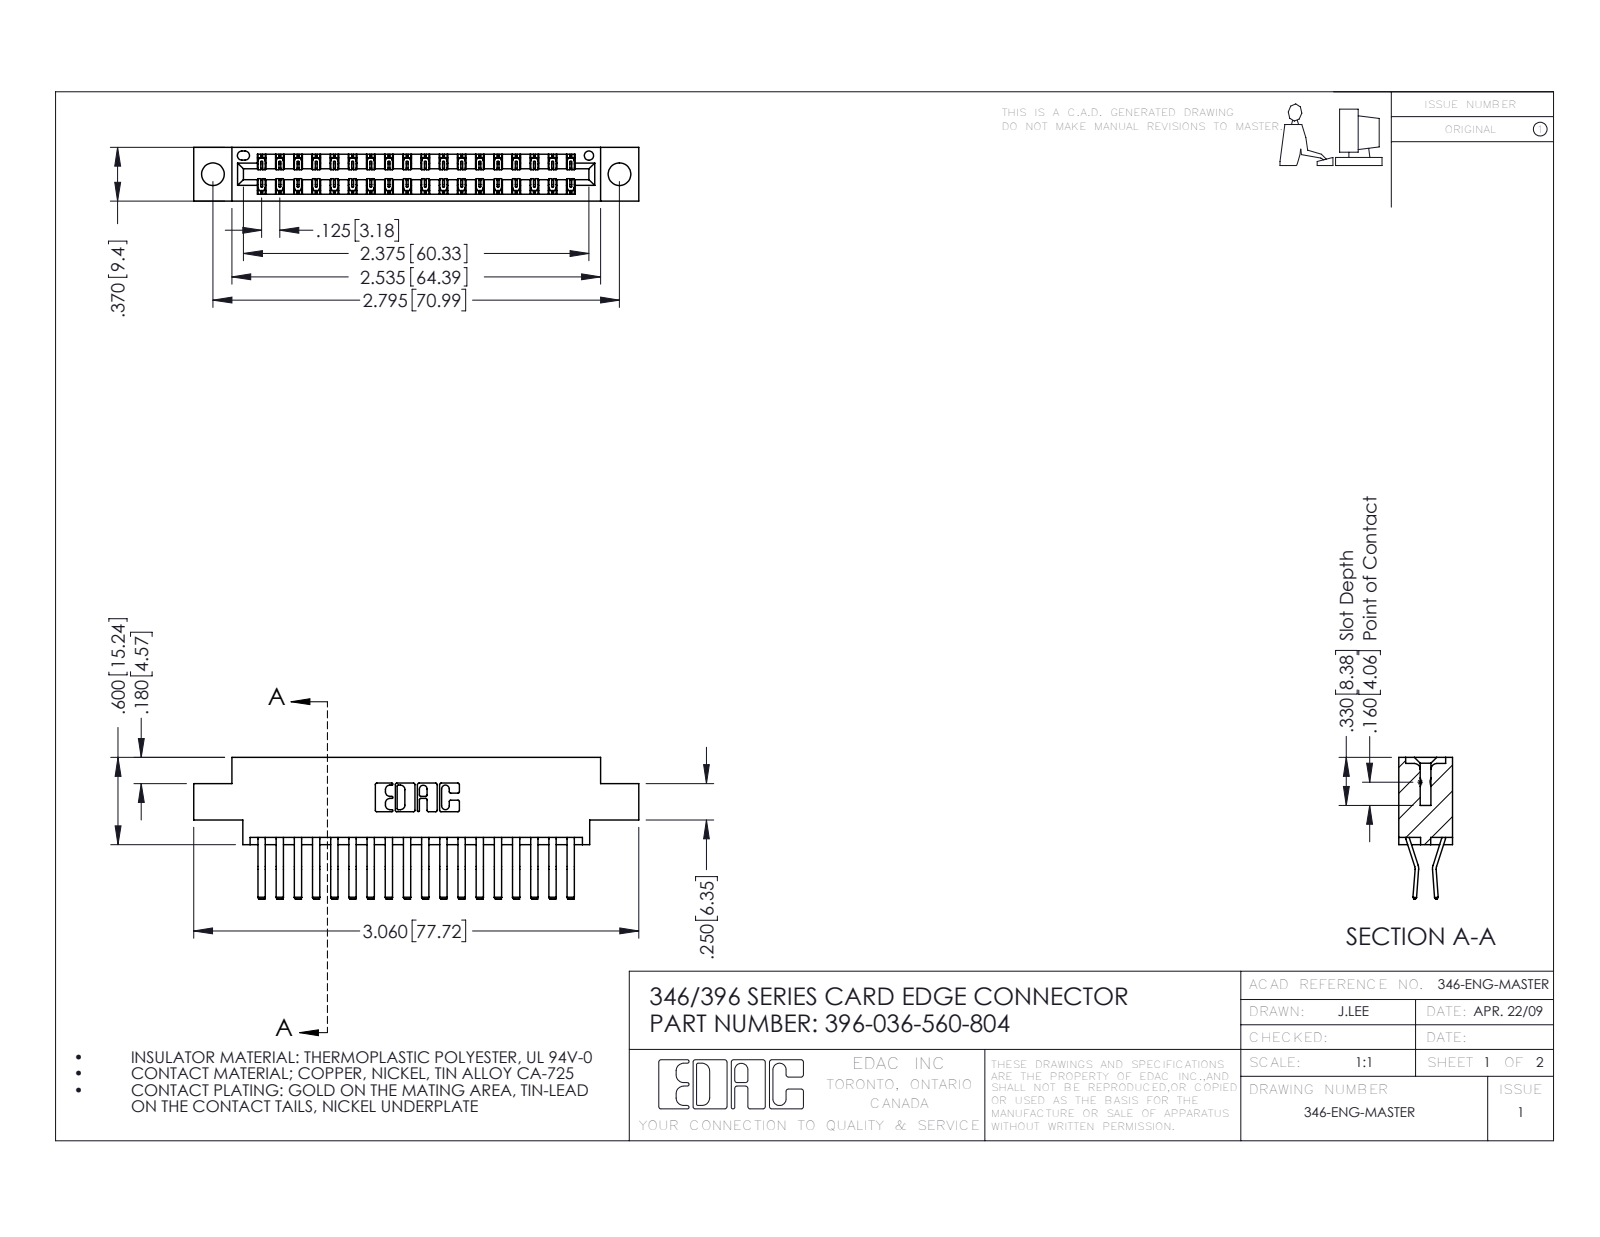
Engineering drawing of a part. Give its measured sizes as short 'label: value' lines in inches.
name: 346 Part_0.170 Offset - 0.156 Dia-TH; 345-292-001_560 Tail; 396-036-560-804
written by: SolidWorks 2016 (CONFIG_CONTROL_DESIGN)
unit: in
bodies: 37 solids, 2070 faces (1340 planar, 730 cylindrical, 0 other)
size: 3.06 × 0.975 × 0.37
volume: 0.451 in³; area: 16.12 in²
holes: 2× ⌀0.156, 1× ⌀0.064
rounds: 54× R0.006, 22× R0.01, 6× R0.007, 6× R0.031, 3× R0.026, 2× R0.01, 2× R0.014, 2× R0.022
face distances: 0.048, 0.322, 0.37, 0.25, 0.025, 0.072, 0.298, 0.275, 0.148, 0.222
hole spacings: 0.246, 2.588, 2.795
